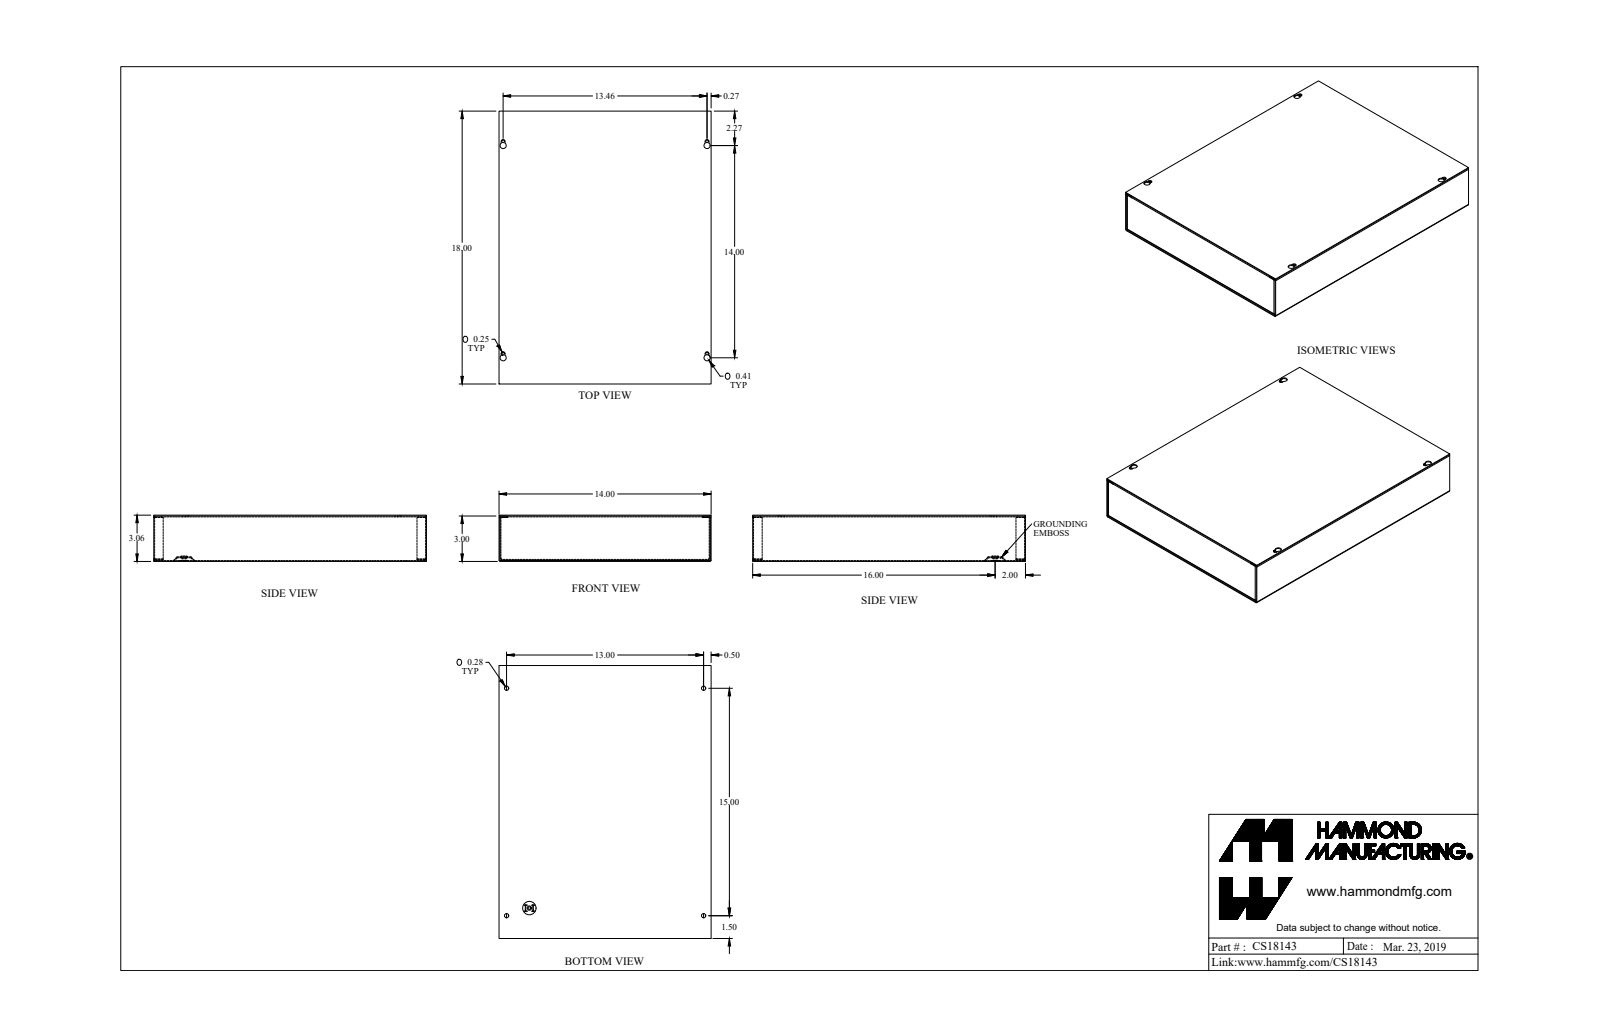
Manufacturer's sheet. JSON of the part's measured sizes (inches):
{"part_name": "CS18143_Default", "step_written_by": "SolidWorks 2019 (CONFIG_CONTROL_DESIGN)", "units": "inches", "bodies": {"solids": 4, "faces": 205, "planar": 125, "cylindrical": 72, "other": 8}, "overall_size": [18, 14, 3.057], "volume_in3": 41.94, "surface_area_in2": 1485, "round_holes": [[0.17, 5], [0.281, 4], [0.5, 1]], "round_bosses_or_shafts": [[0.492, 1], [0.284, 1]], "partial_cylinders_radius": [[0.029, 12], [0.086, 12], [0.057, 8], [0.125, 4], [0.203, 4]], "face_to_face_distances": [0.057, 3, 2.943, 3.057, 13.943, 17.943, 14, 13.886, 18, 17.886], "hole_center_spacings": [0.55, 13.239, 14.502, 19.629, 13, 13.46, 14, 15]}
